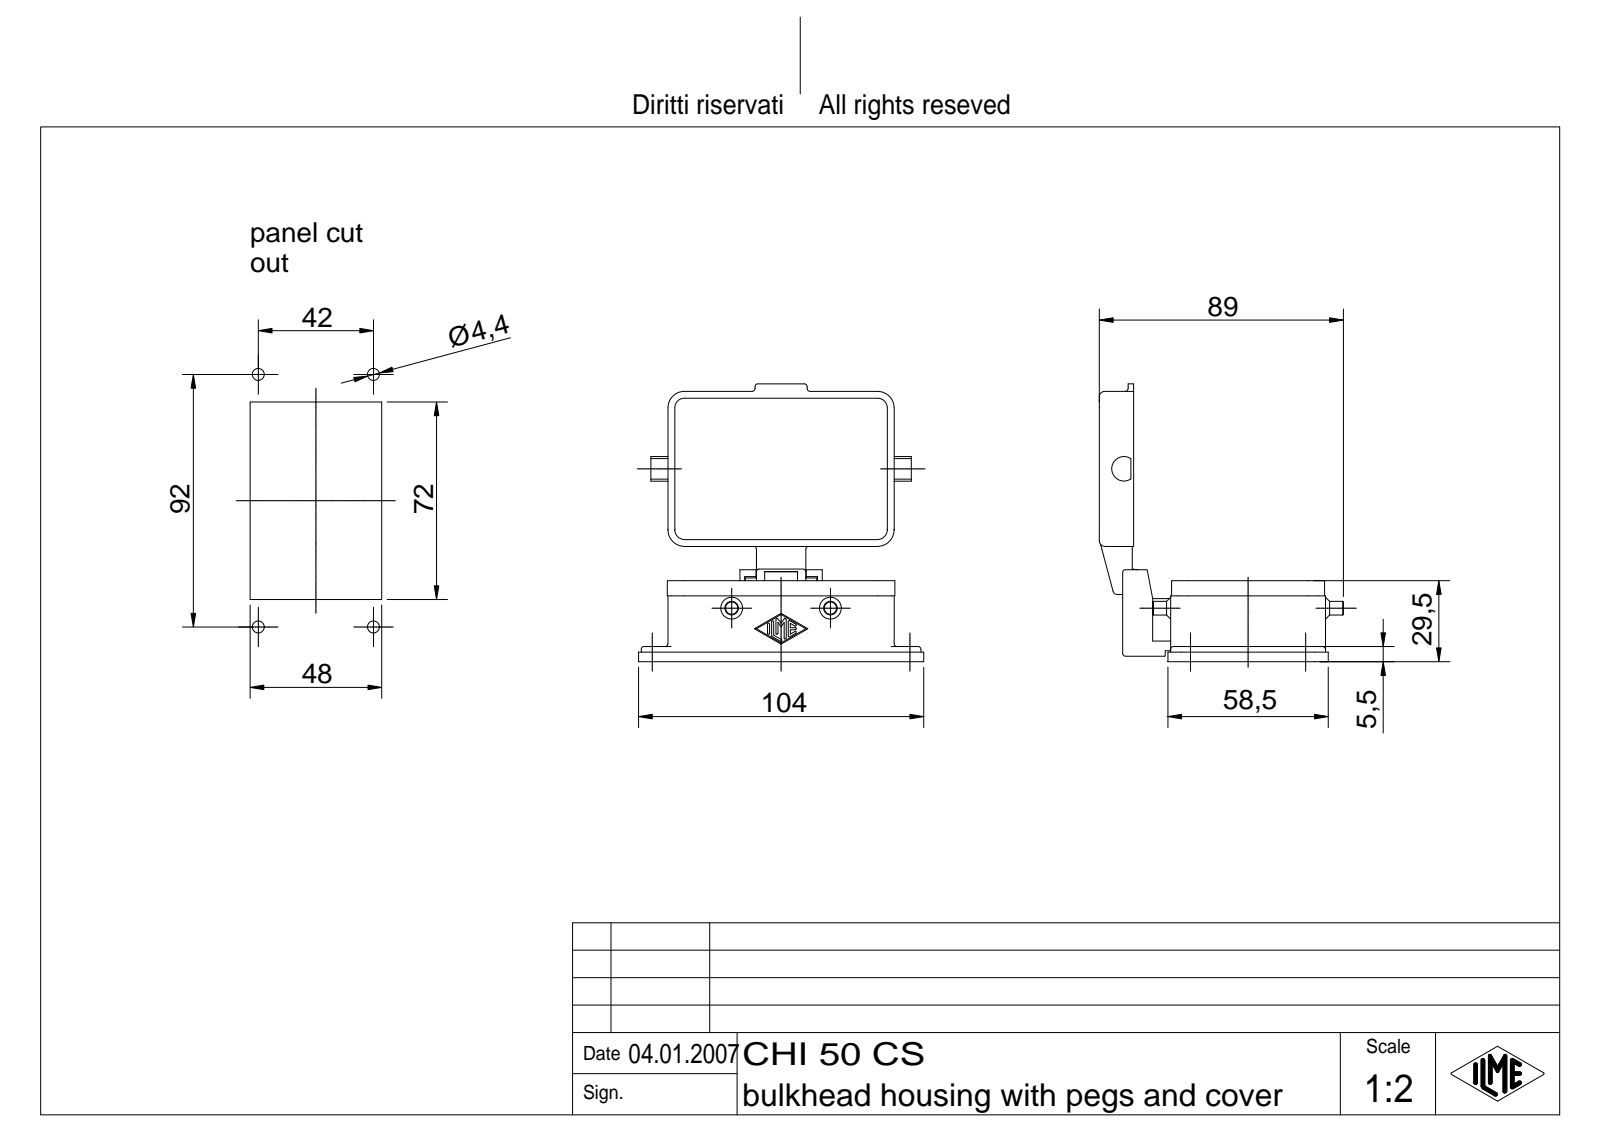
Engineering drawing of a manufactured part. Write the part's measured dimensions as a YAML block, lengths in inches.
part_name: "CHI_50_CS"
step_written_by: "PTC Creo Elements/Direct Modeling 19.0E 27-Jun-2016 (C) Parametric Technology GmbH (AUTOMOTIVE_DESIGN)"
units: inches
bodies: {solids: 1, faces: 386, planar: 184, cylindrical: 156, other: 46}
overall_size: [4.094, 3.986, 3.504]
volume: 4.231
surface_area: 66.9
round_holes:
  - {diameter: 0.097, count: 8}
  - {diameter: 0.122, count: 8}
  - {diameter: 0.173, count: 4}
  - {diameter: 0.157, count: 1}
round_bosses_or_shafts:
  - {diameter: 0.197, count: 2}
  - {diameter: 0.276, count: 1}
  - {diameter: 0.157, count: 1}
partial_cylinders:
  - {radius: 0.039, count: 23}
  - {radius: 0.015, count: 14}
  - {radius: 0.236, count: 12}
  - {radius: 0.059, count: 8}
  - {radius: 0.079, count: 8}
  - {radius: 0.098, count: 4}
  - {radius: 0.118, count: 4}
  - {radius: 0.138, count: 4}
face_to_face_distances: [0.138, 0.118, 0.157, 2.106, 3.13, 3.248, 2.224, 0.098, 0.335, 3.11]
hole_center_spacings: [0.513, 0.63, 0.843, 0.945, 1.109, 1.693, 2.598, 2.674]
